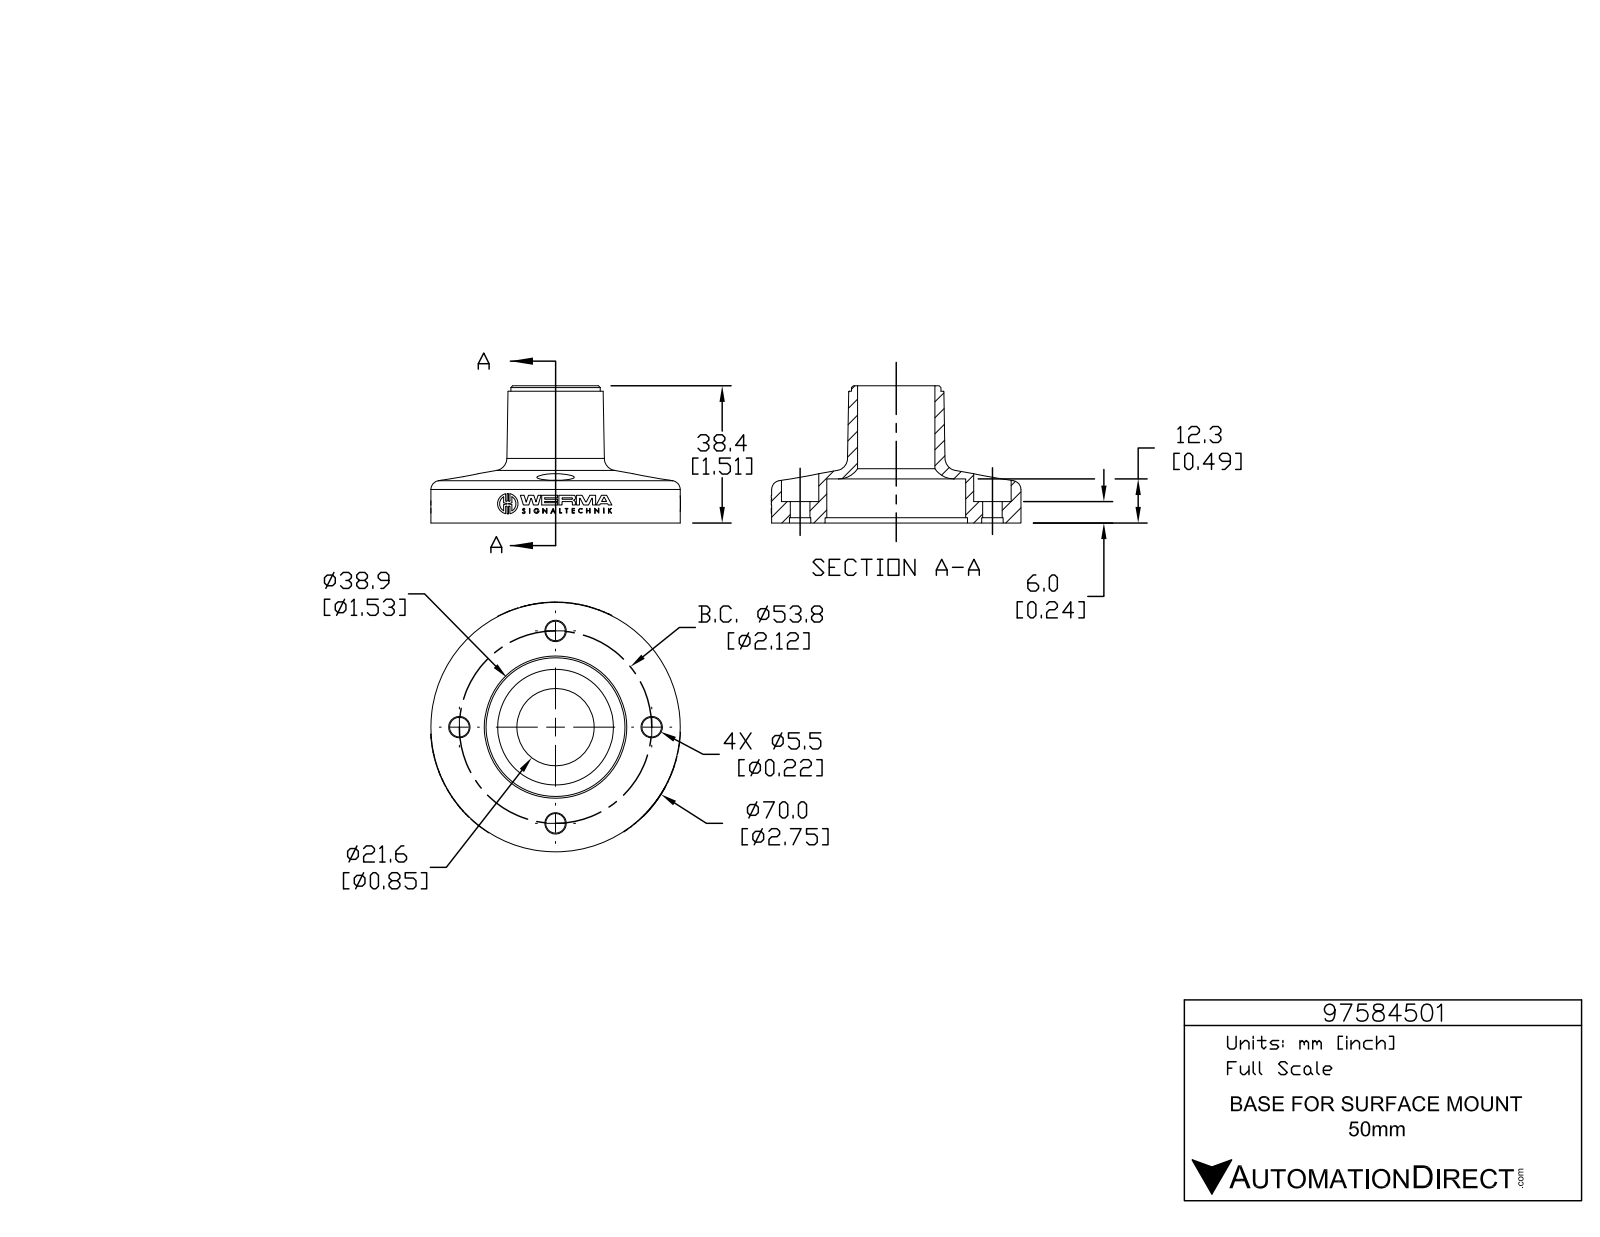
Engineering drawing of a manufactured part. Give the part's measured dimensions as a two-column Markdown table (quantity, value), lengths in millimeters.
| quantity | value |
| --- | --- |
| part name | 97584501 |
| STEP written by | SolidWorks 2015 (AUTOMOTIVE_DESIGN) |
| units | millimeters |
| bodies | 1 solid, 815 faces (532 planar, 271 cylindrical, 12 other) |
| overall size | 70.1 × 70.1 × 38.5 |
| volume | 37 070 mm³ |
| surface area | 15 610 mm² |
| round holes (diameter × count) | 5.5 × 4, 6 × 4, 10.5 × 4, 1 × 3, 21.7 × 1, 39 × 1, 40 × 1 |
| round bosses / shafts (diameter × count) | 5.7 × 3, 1.4 × 3, 70 × 1, 25.1 × 1 |
| partial cylindrical surfaces (radius × count) | 0.2 × 6, 0.2 × 6, 0.2 × 6, 3.3 × 6, 0.1 × 3, 0.1 × 3, 0.2 × 3, 0.2 × 3 |
| main face-to-face distances | 12.4, 6.4, 6, 1.5, 37, 26.1, 32.5, 38.5, 10.9, 4.5 |
| hole center spacings | 27, 38.2, 54 |
